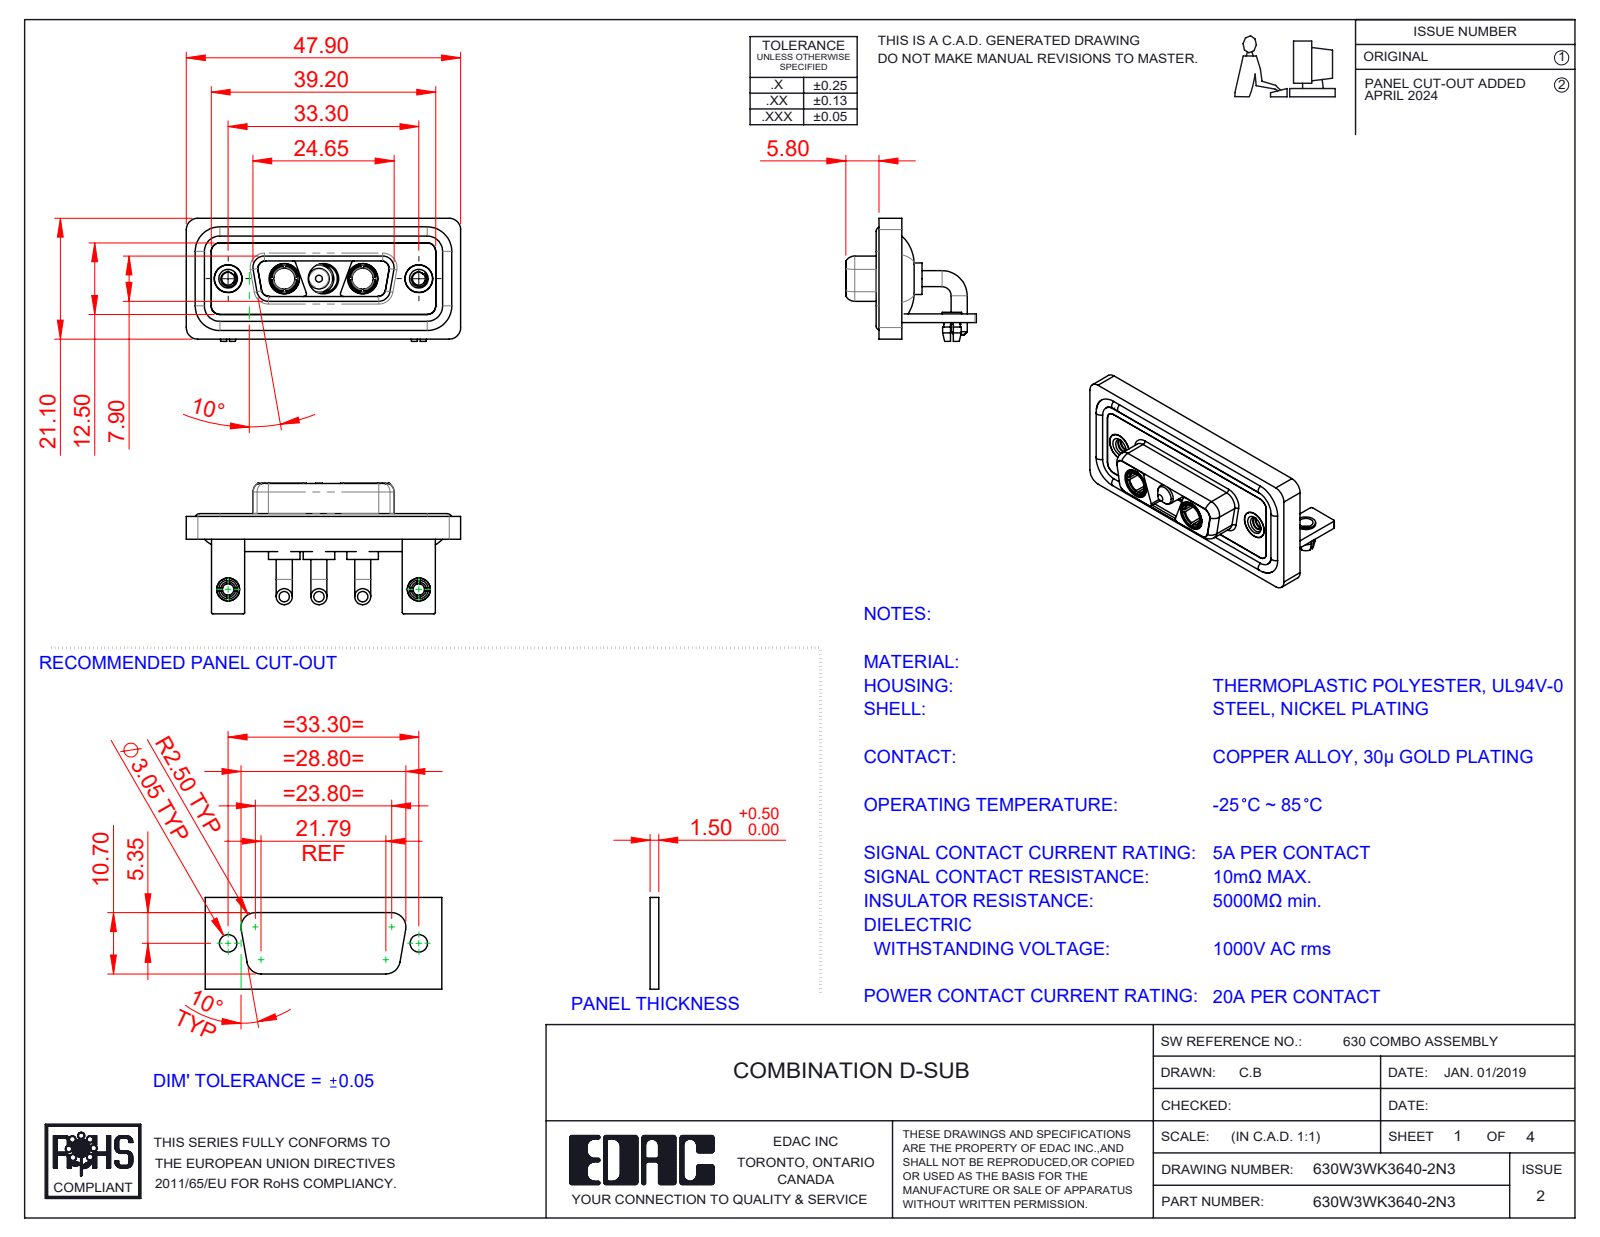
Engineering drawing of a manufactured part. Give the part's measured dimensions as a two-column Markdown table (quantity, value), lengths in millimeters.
| quantity | value |
| --- | --- |
| part name | 630Combo Threaded Rivet_2; 630Combo Housing_3WK3; 630Combo Stabilizer Bracket_50 Contacts; 630Combo Shell Front_15 Contacts (+6 more) |
| STEP written by | SolidWorks 2023 (CONFIG_CONTROL_DESIGN) |
| units | millimeters |
| bodies | 17 solids, 735 faces (246 planar, 320 cylindrical, 169 other) |
| overall size | 47.9 × 22.8 × 21.5 |
| volume | 6 435 mm³ |
| surface area | 10 684 mm² |
| round holes (diameter × count) | 4.85 × 5, 5.3 × 3, 2 × 2, 2.26 × 2, 2.5 × 2, 3.2 × 2, 3.7 × 2, 4 × 2, 4.05 × 2, 5 × 2 |
| round bosses / shafts (diameter × count) | 2.8 × 6, 1.6 × 4, 5.5 × 3, 5.2 × 3, 4.75 × 3, 3.75 × 3, 4.96 × 2, 4.95 × 2 |
| partial cylindrical surfaces (radius × count) | 2 × 21, 1.5 × 18, 0.25 × 16, 1.35 × 12, 0.5 × 9, 1.6 × 8, 0.6 × 4, 0.65 × 4 |
| main face-to-face distances | 0.4, 2.9, 1.5, 3.7, 1.8, 1.1, 4.1, 1.6, 2.5, 1.4 |
| hole center spacings | 6.85, 9.8, 16.65, 23.5, 33.3, 13.7 |
